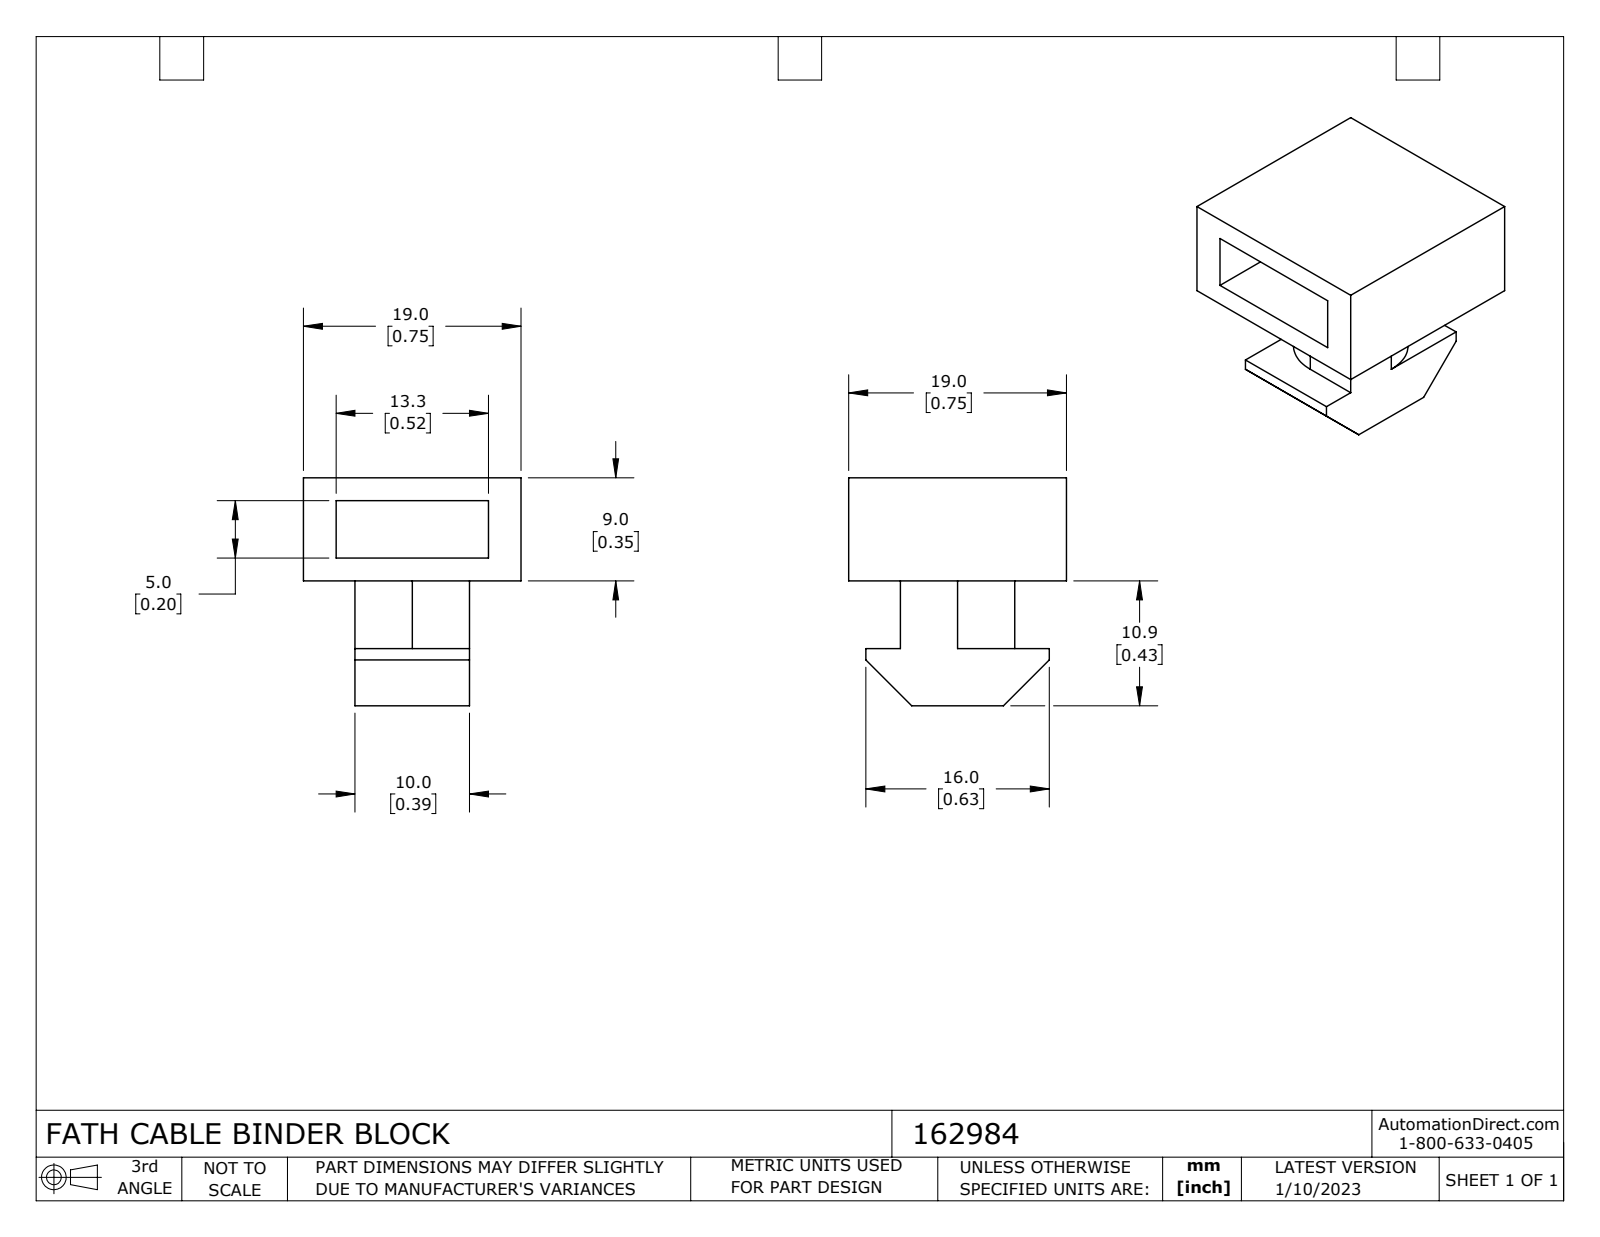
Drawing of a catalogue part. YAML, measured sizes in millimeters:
part_name: "162984"
step_written_by: "SolidWorks 2021 (CONFIG_CONTROL_DESIGN)"
units: millimeters
bodies: {solids: 1, faces: 23, planar: 21, cylindrical: 2, other: 0}
overall_size: [19.9, 19, 19]
volume: 3150
surface_area: 2502
partial_cylinders:
  - {radius: 5, count: 1}
face_to_face_distances: [2, 7, 5, 19, 9, 4.5, 14.5, 2.8, 16.2, 1.7]
